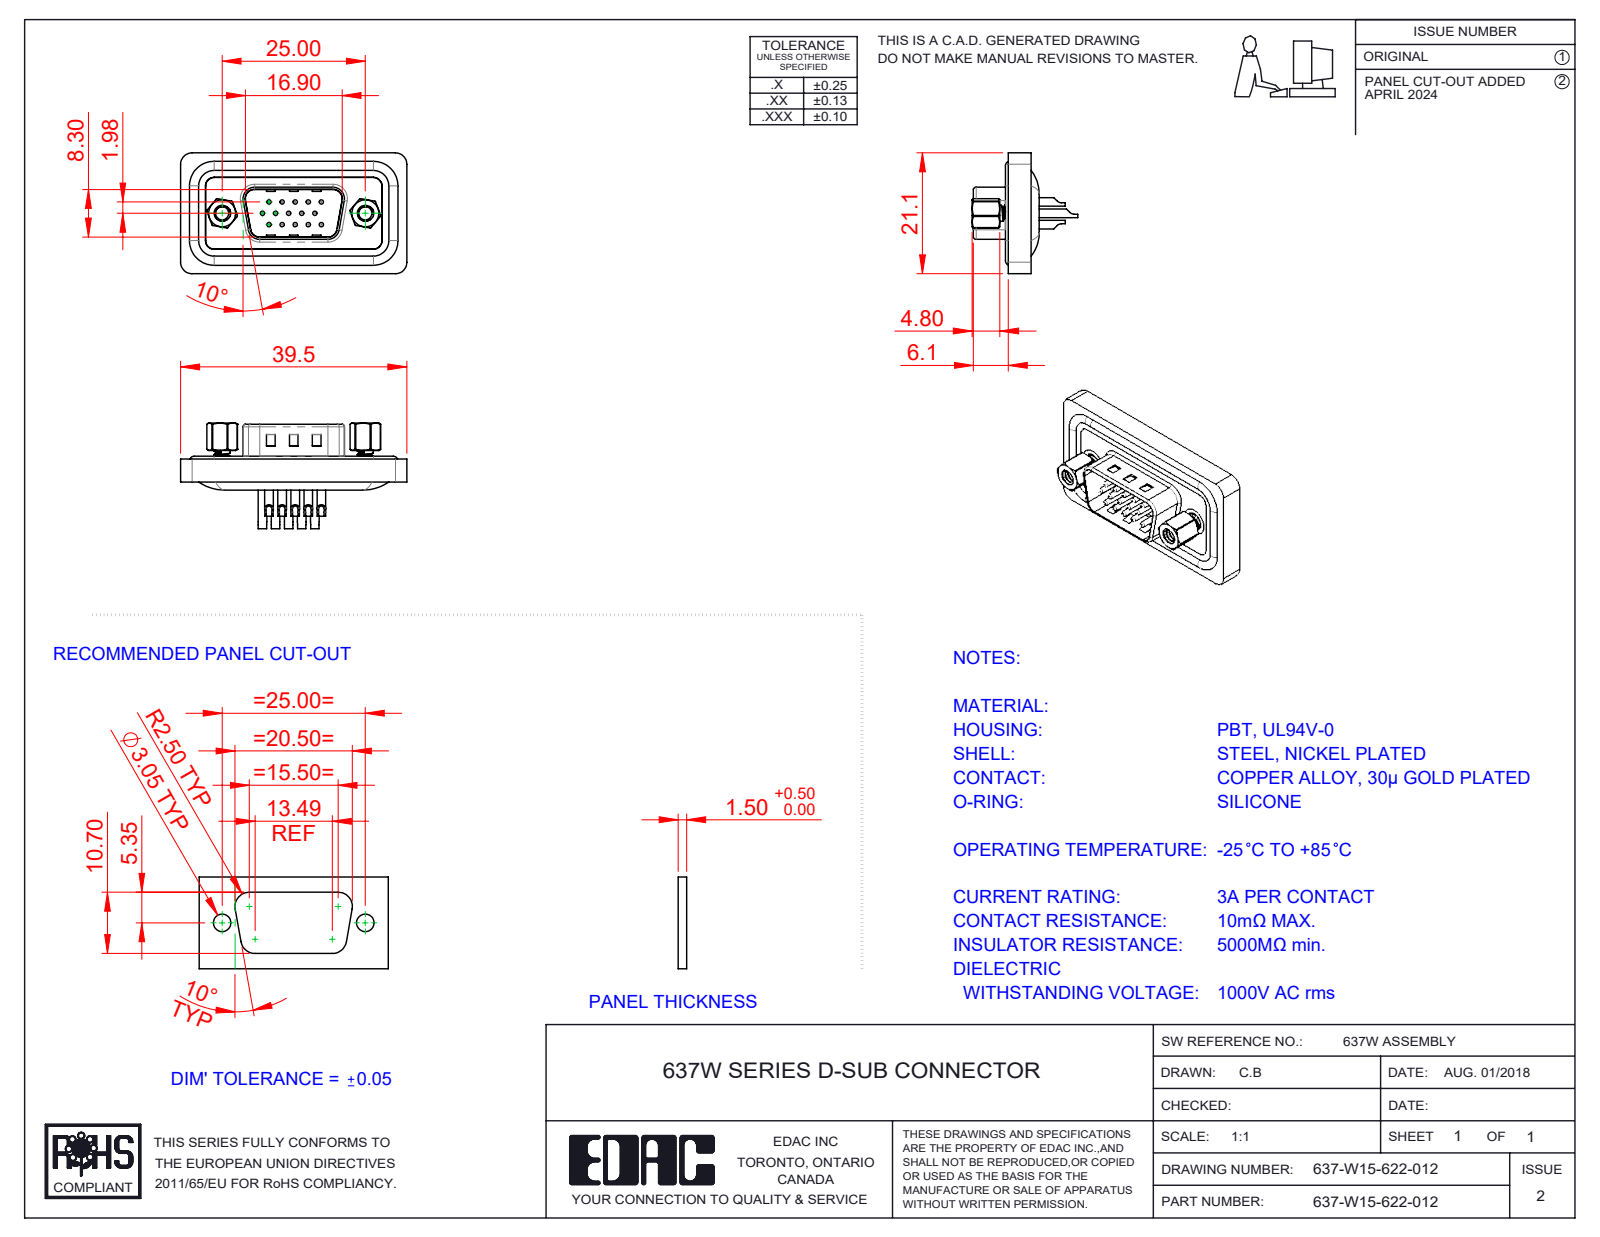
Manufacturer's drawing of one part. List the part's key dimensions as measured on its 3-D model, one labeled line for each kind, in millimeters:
Part name (STEP PRODUCT): 637W Shell_15 Contacts; 637W Housing_15 Contacts; 637W 4-40 Hex Standoff; 637W 4-40 Threaded Rivet (+5 more)
STEP written by: SolidWorks 2016 (CONFIG_CONTROL_DESIGN)
Units: millimetres
Bodies: 23 solids, 1031 faces (276 planar, 478 cylindrical, 277 other)
Overall size (bounding box): 39.51 × 21.1 × 18.25
Volume: 4 052 mm³ · Surface area: 7 010 mm²
Round holes (diameter × count): ⌀0.75 ×15, ⌀1 ×15, ⌀1.5 ×15, ⌀1.6 ×15, ⌀2 ×15, ⌀2.26 ×2, ⌀2.29 ×2, ⌀4 ×2, ⌀4.8 ×2, ⌀5 ×2
Round bosses / shafts (diameter × count): ⌀1.5 ×8, ⌀1.6 ×4, ⌀4.9 ×2, ⌀2.79 ×2, ⌀5 ×1
Partial cylindrical surfaces — rounded edges, fillets, slot ends (radius × count): R1.5 ×14, R2 ×14, R0.5 ×8, R2.7 ×6, R0.9 ×4, R1.6 ×4, R4.3 ×4, R1 ×3
Main face-to-face distances: 0.4, 1.1, 2.9, 1.6, 2.5, 0.5, 4, 3.6, 0.7, 4.3
Hole centre spacings: 3.96, 2.28, 4.57, 2.29, 6.05, 6.04, 7.92, 6.86
